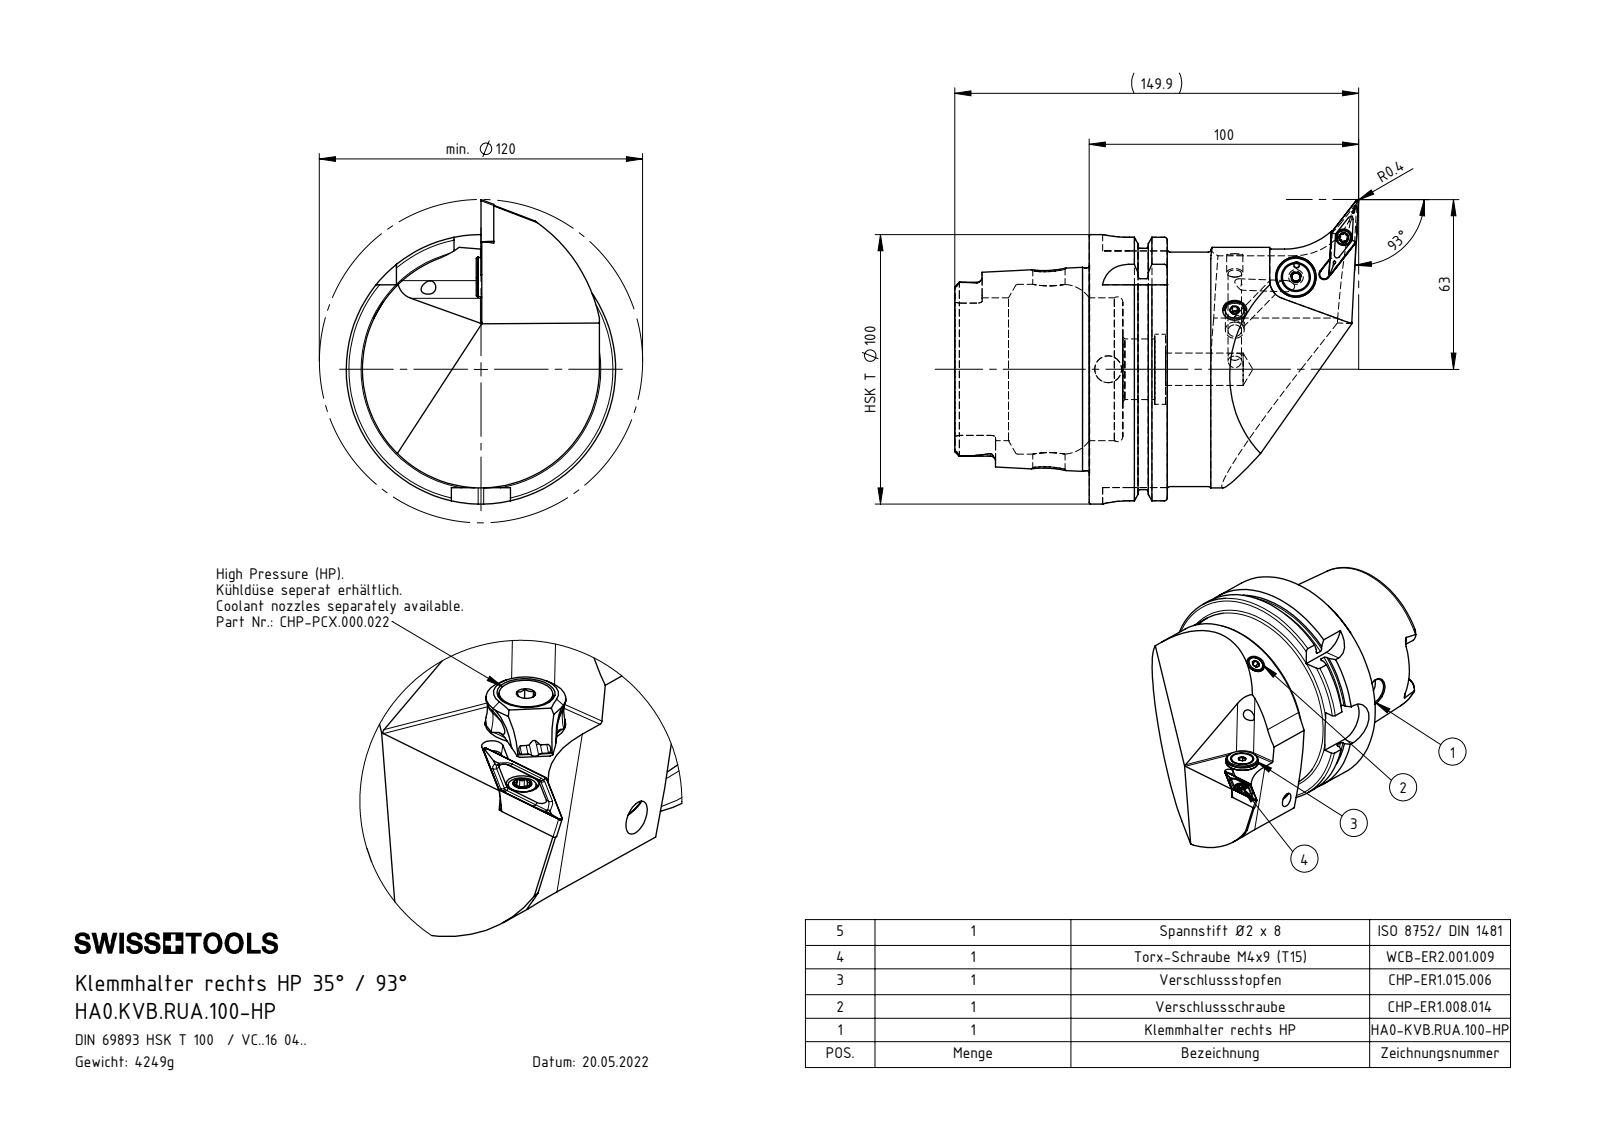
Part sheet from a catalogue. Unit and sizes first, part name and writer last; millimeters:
Units: millimetres
Overall size (bounding box): 149.9 × 113 × 100
Round holes (diameter × count): ⌀5 ×3, ⌀4.2 ×2, ⌀12 ×2, ⌀1.2 ×1, ⌀2 ×1, ⌀2.5 ×1, ⌀3 ×1, ⌀3.3 ×1, ⌀4.4 ×1, ⌀5.2 ×1, ⌀6.1 ×1, ⌀7 ×1
Round bosses / shafts (diameter × count): ⌀100 ×1, ⌀91.95 ×1, ⌀87 ×1, ⌀75.26 ×1, ⌀15 ×1, ⌀13.4 ×1, ⌀10 ×1, ⌀8 ×1
Partial cylindrical surfaces — rounded edges, fillets, slot ends (radius × count): R0.34 ×6, R0.59 ×6, R1.9 ×6, R10 ×4, R0.5 ×2, R4.83 ×2, R4.88 ×2, R1.75 ×1
Main face-to-face distances: 12.45, 28.95, 16.5, 49.9, 62.35, 78.85, 43.7, 87.8, 78.2, 28.3
Hole centre spacings: 4.5, 20.26, 20.35, 23.02, 23.12, 77.68, 79.96, 100.22
Volume: 540 696 mm³ · Surface area: 70 802 mm²
Bodies: 10 solids, 453 faces (118 planar, 129 cylindrical, 206 other)
Part name (STEP PRODUCT): HA0-KVB.RUA.100-HP_A_Fertigbearbeitung; CHP-ER1.015.006; VCMT160404; CHP-ER1.015.006_A (+7 more)
STEP written by: SolidWorks 2017 (AUTOMOTIVE_DESIGN)
